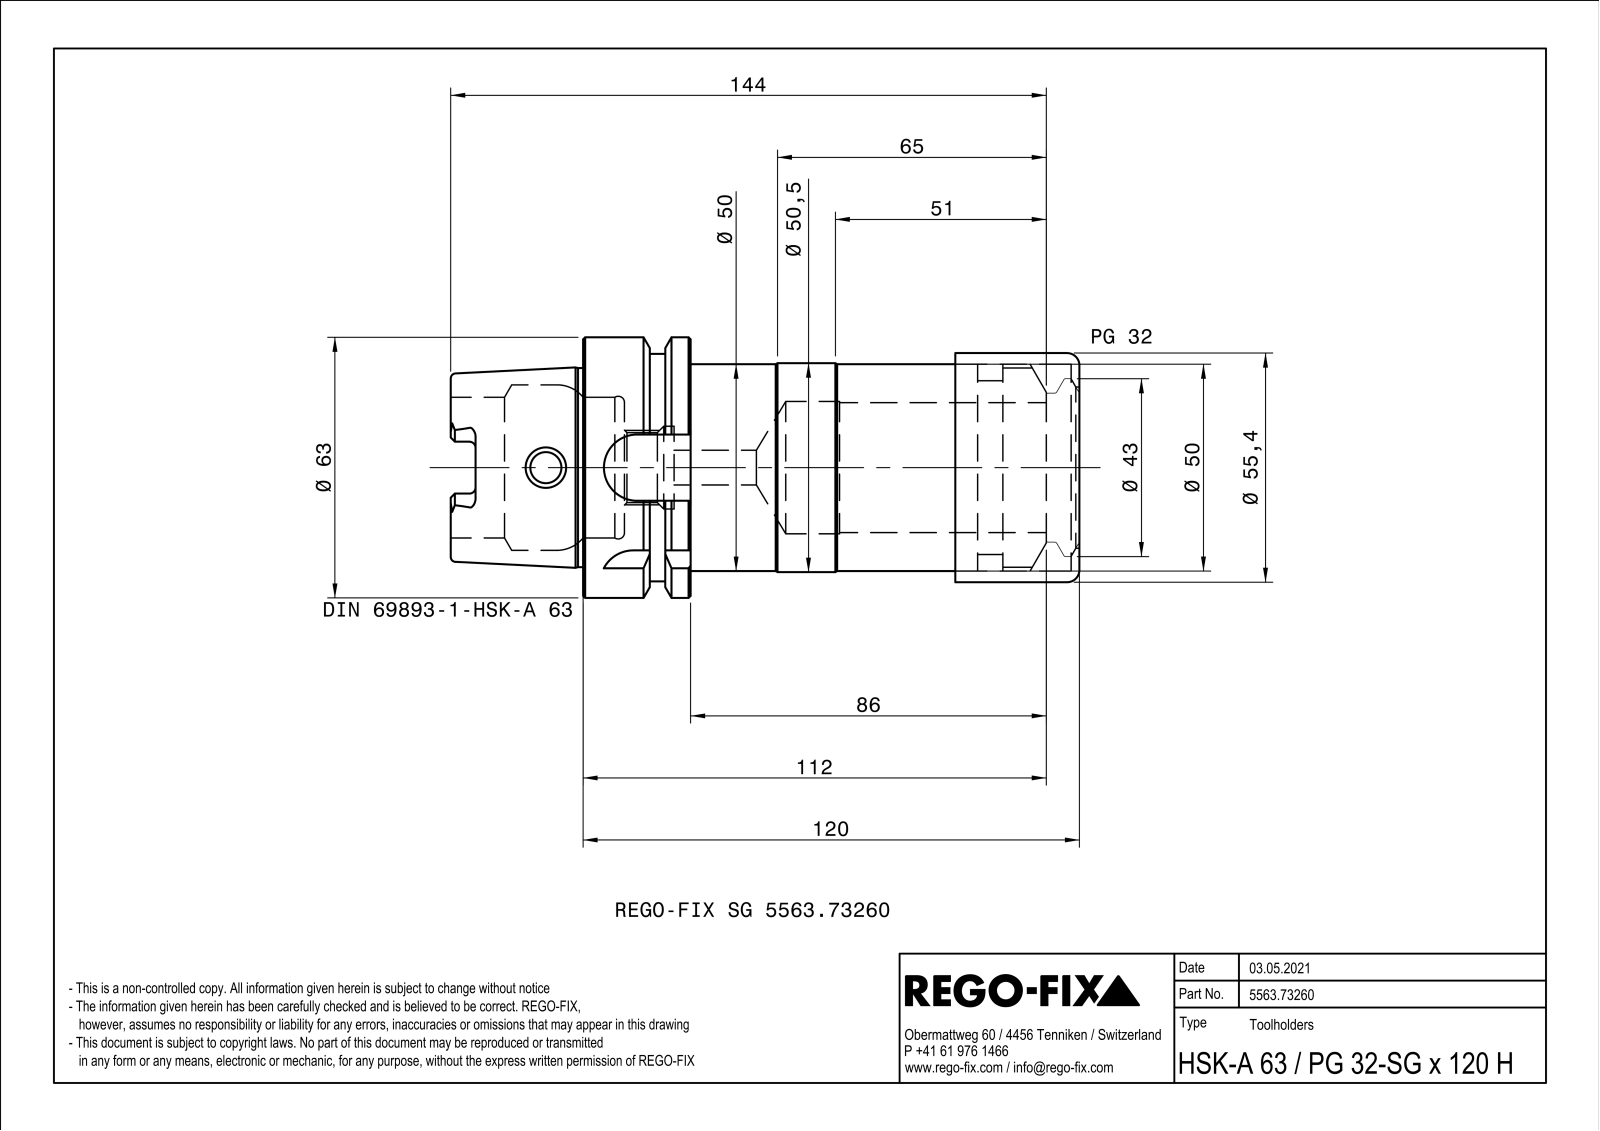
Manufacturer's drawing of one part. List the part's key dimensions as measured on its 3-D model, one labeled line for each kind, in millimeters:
Part name (STEP PRODUCT): 0008432
STEP written by: SIEMENS PLM Software Solid Edge ST10 (AUTOMOTIVE_DESIGN)
Units: millimetres
Bodies: 1 solid, 161 faces (54 planar, 45 cylindrical, 62 other)
Overall size (bounding box): 152 × 63 × 63
Volume: 204 210 mm³ · Surface area: 52 918 mm²
Round holes (diameter × count): ⌀7.5 ×2, ⌀8.4 ×1, ⌀9 ×1, ⌀10 ×1, ⌀16.92 ×1, ⌀20 ×1, ⌀33 ×1, ⌀34 ×1, ⌀38.25 ×1, ⌀40 ×1, ⌀48.38 ×1, ⌀50.05 ×1
Round bosses / shafts (diameter × count): ⌀63 ×1, ⌀55 ×1, ⌀50.5 ×1, ⌀50 ×1, ⌀49.3 ×1, ⌀48.04 ×1, ⌀42 ×1
Partial cylindrical surfaces — rounded edges, fillets, slot ends (radius × count): R1.5 ×6, R2.88 ×4, R8 ×4, R25.38 ×1, R27.12 ×1
Main face-to-face distances: 26, 94, 120, 10, 16, 110, 90, 22, 24.6, 69.4
Hole centre spacings: 22
